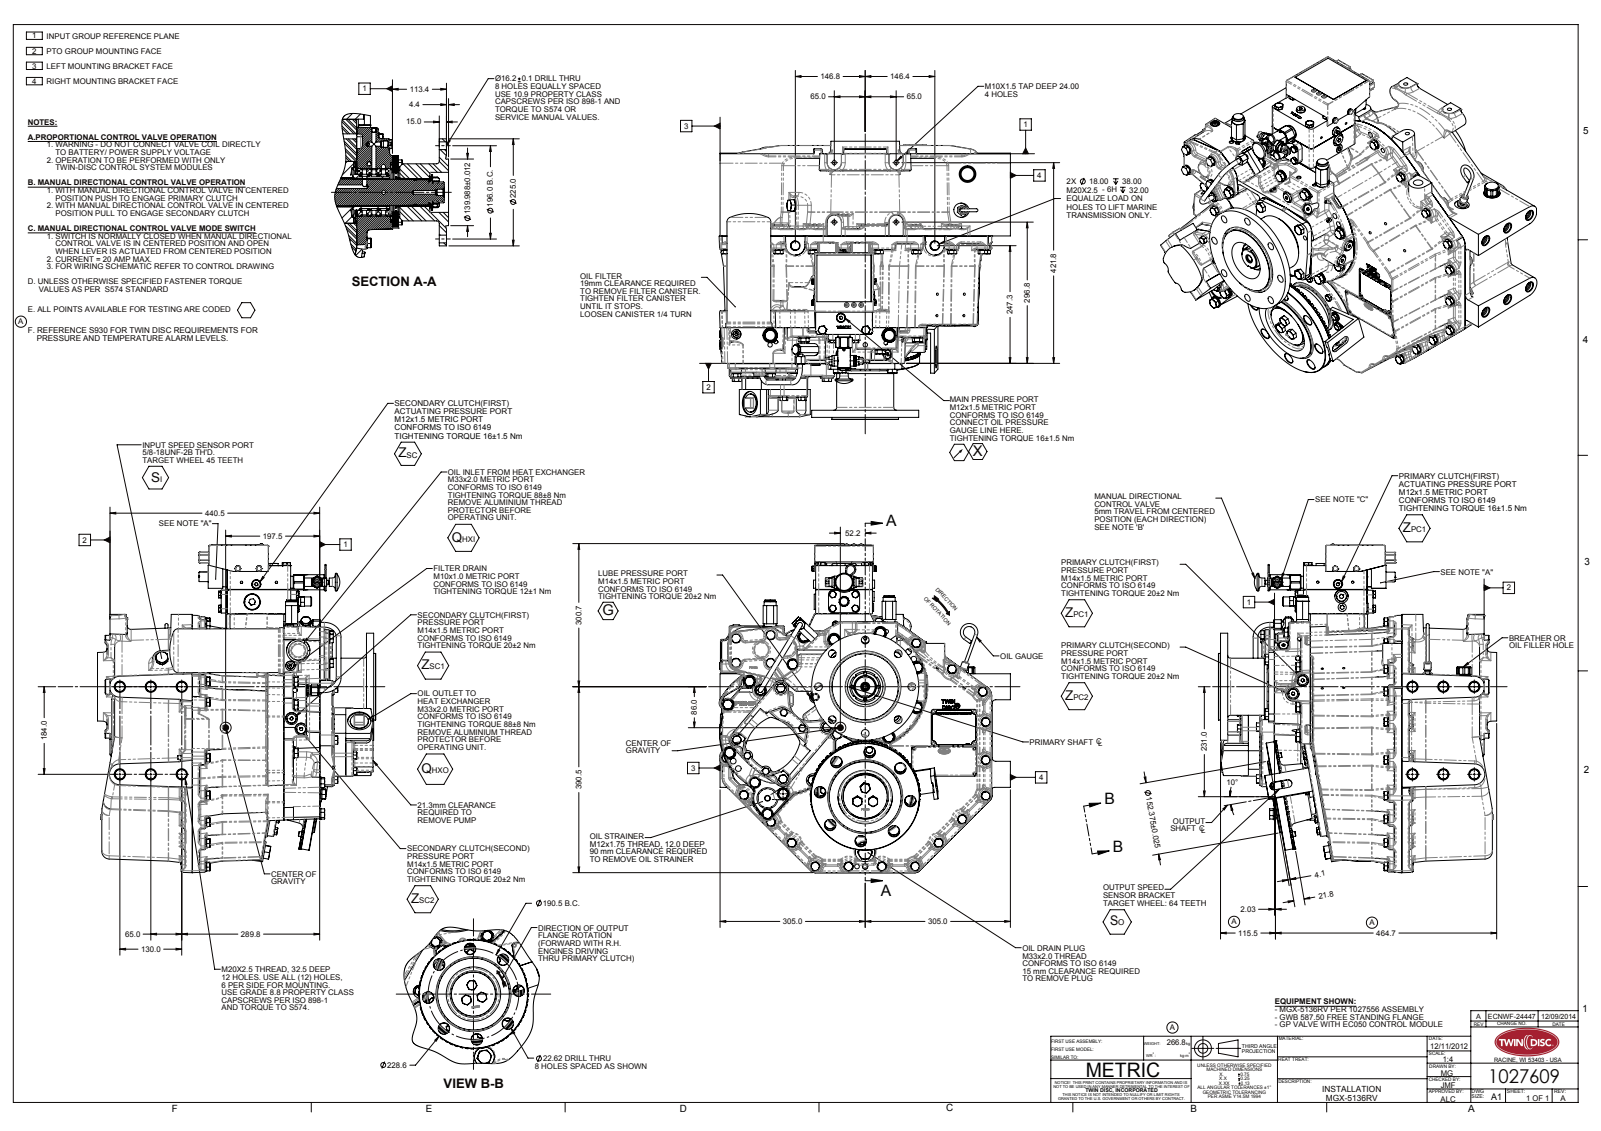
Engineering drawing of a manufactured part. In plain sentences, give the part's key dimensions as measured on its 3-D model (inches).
The part is named "1027609". Its 3-D file was written by "SolidWorks 2010 (CONFIG_CONTROL_DESIGN)". It is 0 solids with 9908 faces: 5998 planar, 1578 cylindrical and 2332 other. Overall it measures 27.218 by 24.091 by 23.015 inches. Round holes: 21 of diameter 0.346, 9 of diameter 0.421, 9 of diameter 0.984, 8 of diameter 0.638, 8 of diameter 0.891, 8 of diameter 0.906, 6 of diameter 0.817, 5 of diameter 0.394, 4 of diameter 0.189, 4 of diameter 0.197, 4 of diameter 0.787, 3 of diameter 0.304. Round bosses or shafts: 26 of diameter 0.781, 13 of diameter 0.945, 8 of diameter 0.748, 5 of diameter 0.433, 5 of diameter 0.1, 4 of diameter 0.512, 4 of diameter 0.394, 3 of diameter 0.75. Partial cylindrical surfaces (rounded edges, fillets, slot ends): 135 of radius 0.118, 77 of radius 0.315, 61 of radius 0.256, 58 of radius 1.563, 49 of radius 0.098, 42 of radius 0.236, 40 of radius 0.079, 21 of radius 0.025. The main face-to-face distances are 0.015, 0.017, 7.589, 7.574, 7.572, 7.557, 10.542, 2.953, 2.968, 10.525. The hole center spacings are 5.303, 6.929, 2.87, 7.5, 2.87, 2.756, 6.929, 2.87.
